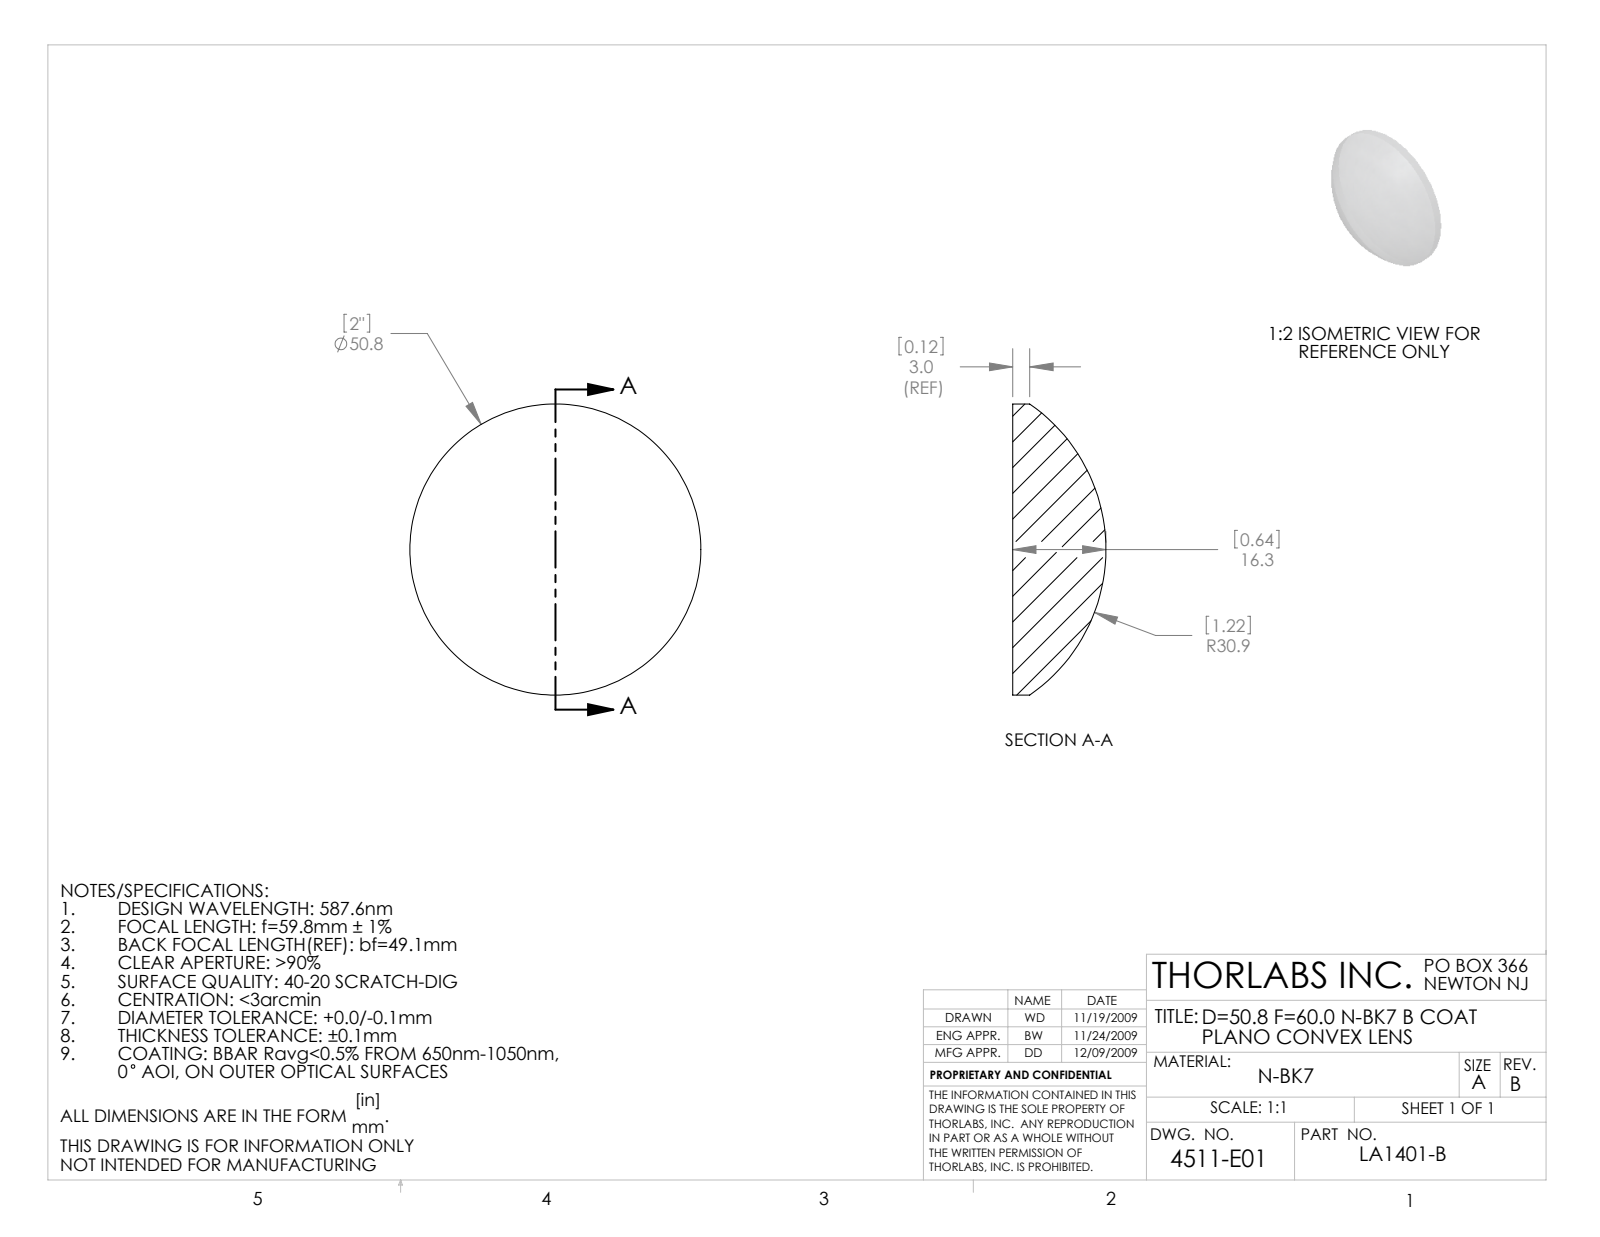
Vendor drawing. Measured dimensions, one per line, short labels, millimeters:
name: 4511-E0W
written by: SolidWorks 2009 (AUTOMOTIVE_DESIGN)
unit: mm
bodies: 1 solid, 5 faces (1 planar, 2 cylindrical, 2 other)
size: 50.8 × 50.8 × 16.29
volume: 20 768 mm³; area: 5 086 mm²
bosses: 1× ⌀50.8
